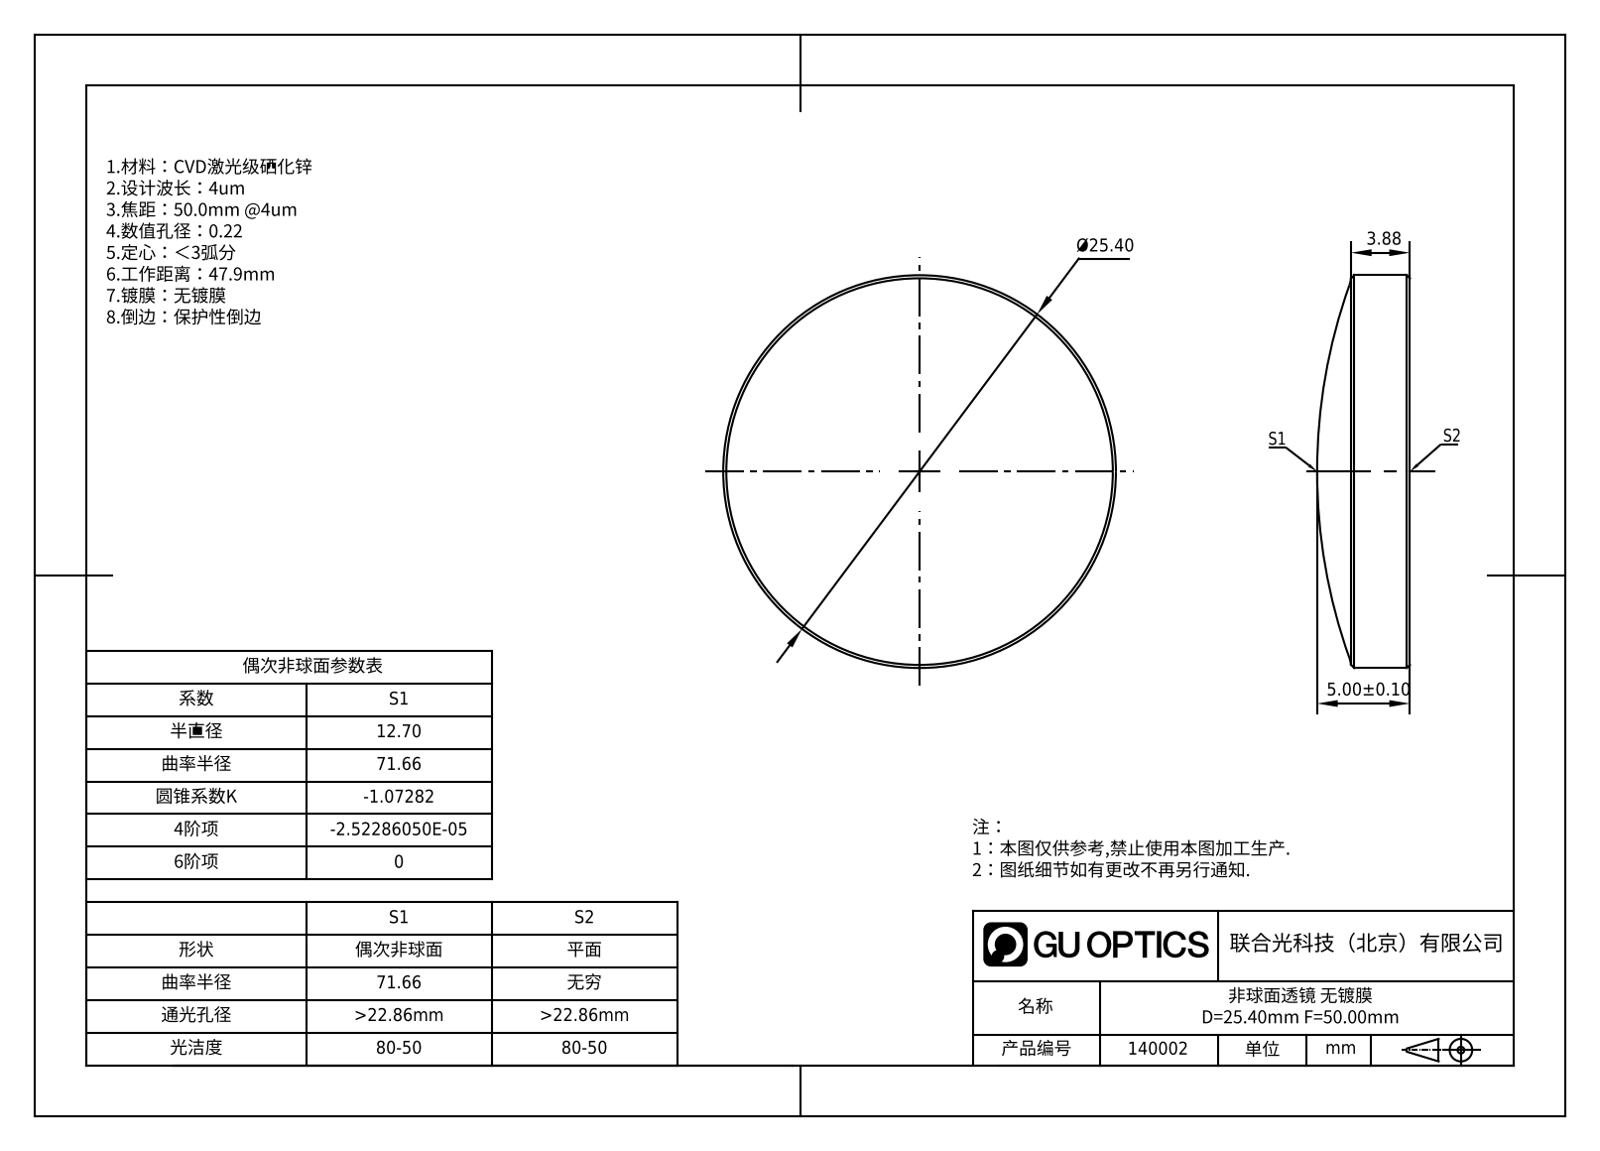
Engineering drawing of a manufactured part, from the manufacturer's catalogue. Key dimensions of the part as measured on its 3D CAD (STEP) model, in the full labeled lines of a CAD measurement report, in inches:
Part name (STEP PRODUCT): GL7AL1-025-050
STEP written by: SolidWorks 2022 (AUTOMOTIVE_DESIGN)
Units: inches
Bodies: 1 solid, 9 faces (1 planar, 2 cylindrical, 6 other)
Overall size (bounding box): 1 × 1 × 0.197
Volume: 0.137 in³ · Surface area: 2.031 in²
Round bosses / shafts (diameter × count): ⌀1 ×1
